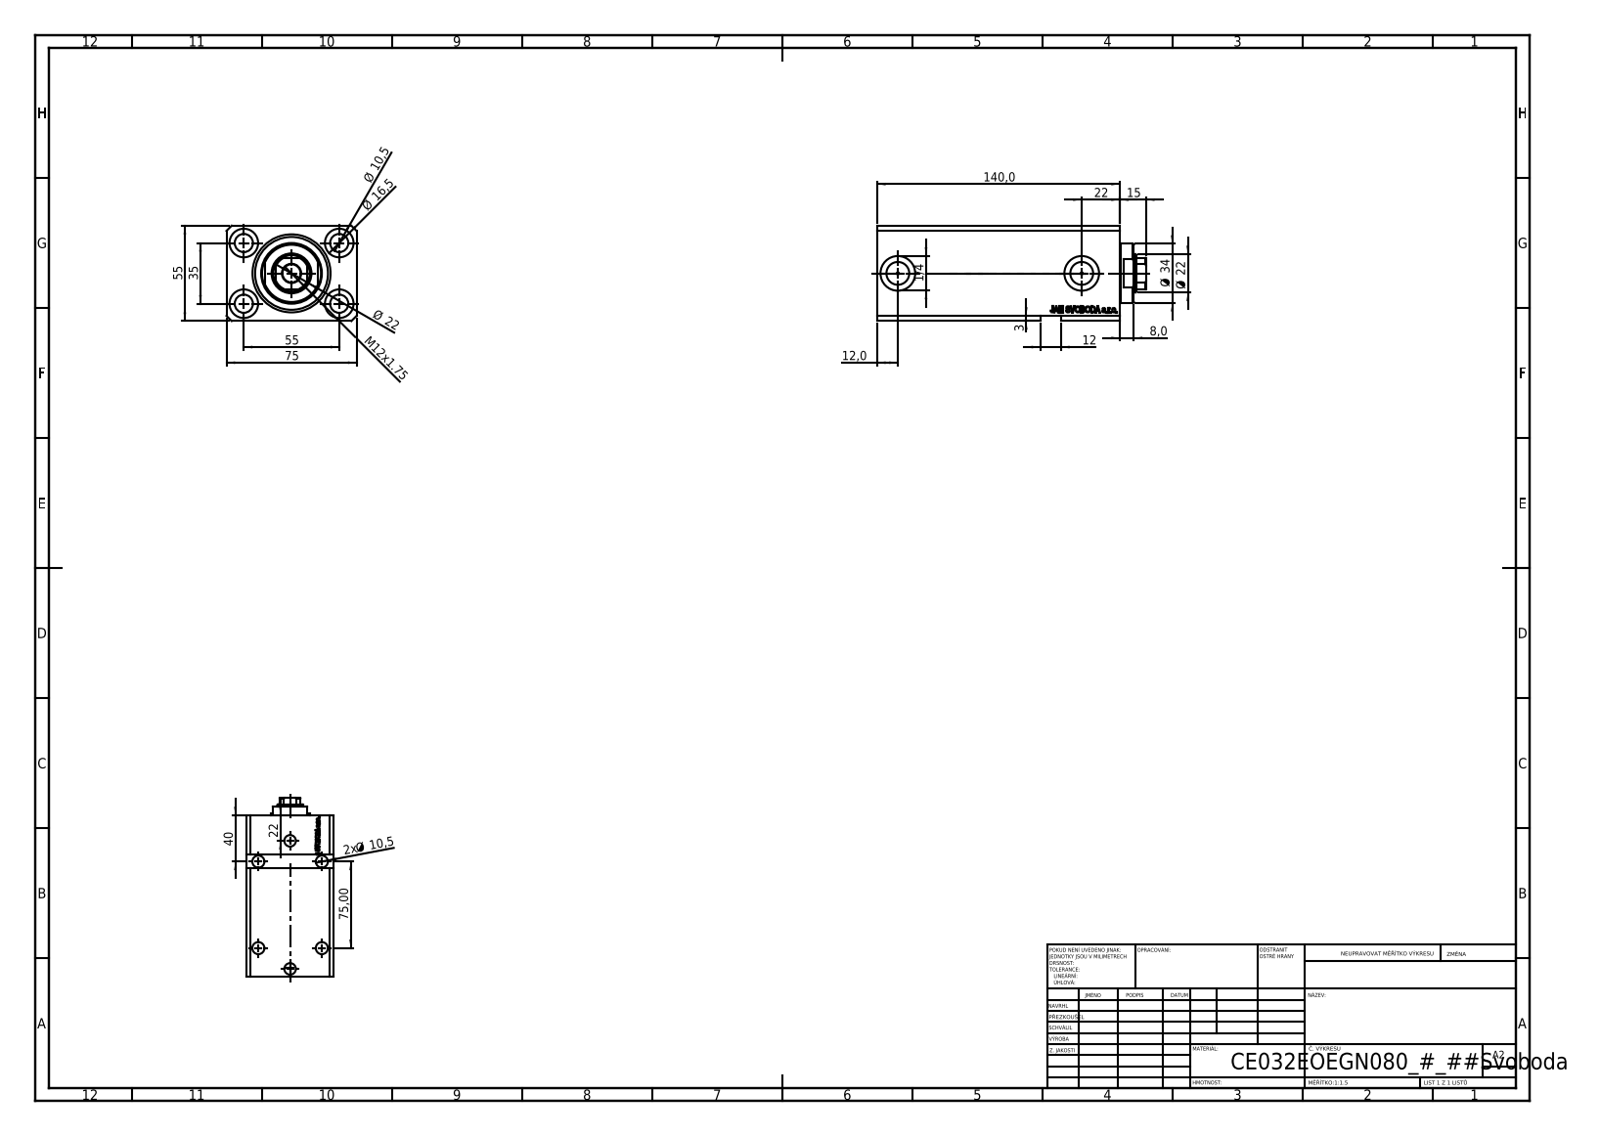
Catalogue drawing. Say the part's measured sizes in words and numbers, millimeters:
The part is named "V250CE_E_Body; V250CE_C_VCP; V250CE_VC_E". Its 3-D file was written by "SolidWorks 2019 (CONFIG_CONTROL_DESIGN)". It is 3 solids with 914 faces: 438 planar, 104 cylindrical and 372 other. Overall it measures 155 by 75 by 55 millimeters. Its volume is 469 209 cubic millimeters and its surface area 102 026 square millimeters. Round holes: 9 of diameter 10.5, 4 of diameter 1.25, 4 of diameter 16.5, 2 of diameter 10, 2 of diameter 13.16, 2 of diameter 20, 1 of diameter 22, 1 of diameter 32, 1 of diameter 45. Round bosses or shafts: 1 of diameter 34. Partial cylindrical surfaces (rounded edges, fillets, slot ends): 1 of radius 10.5. The main face-to-face distances are 55, 75, 15, 140, 125, 9.9, 115.1, 130.1, 11, 129. The hole center spacings are 32.6, 32.87, 55, 96.98, 32.58, 35, 65.19, 75.
